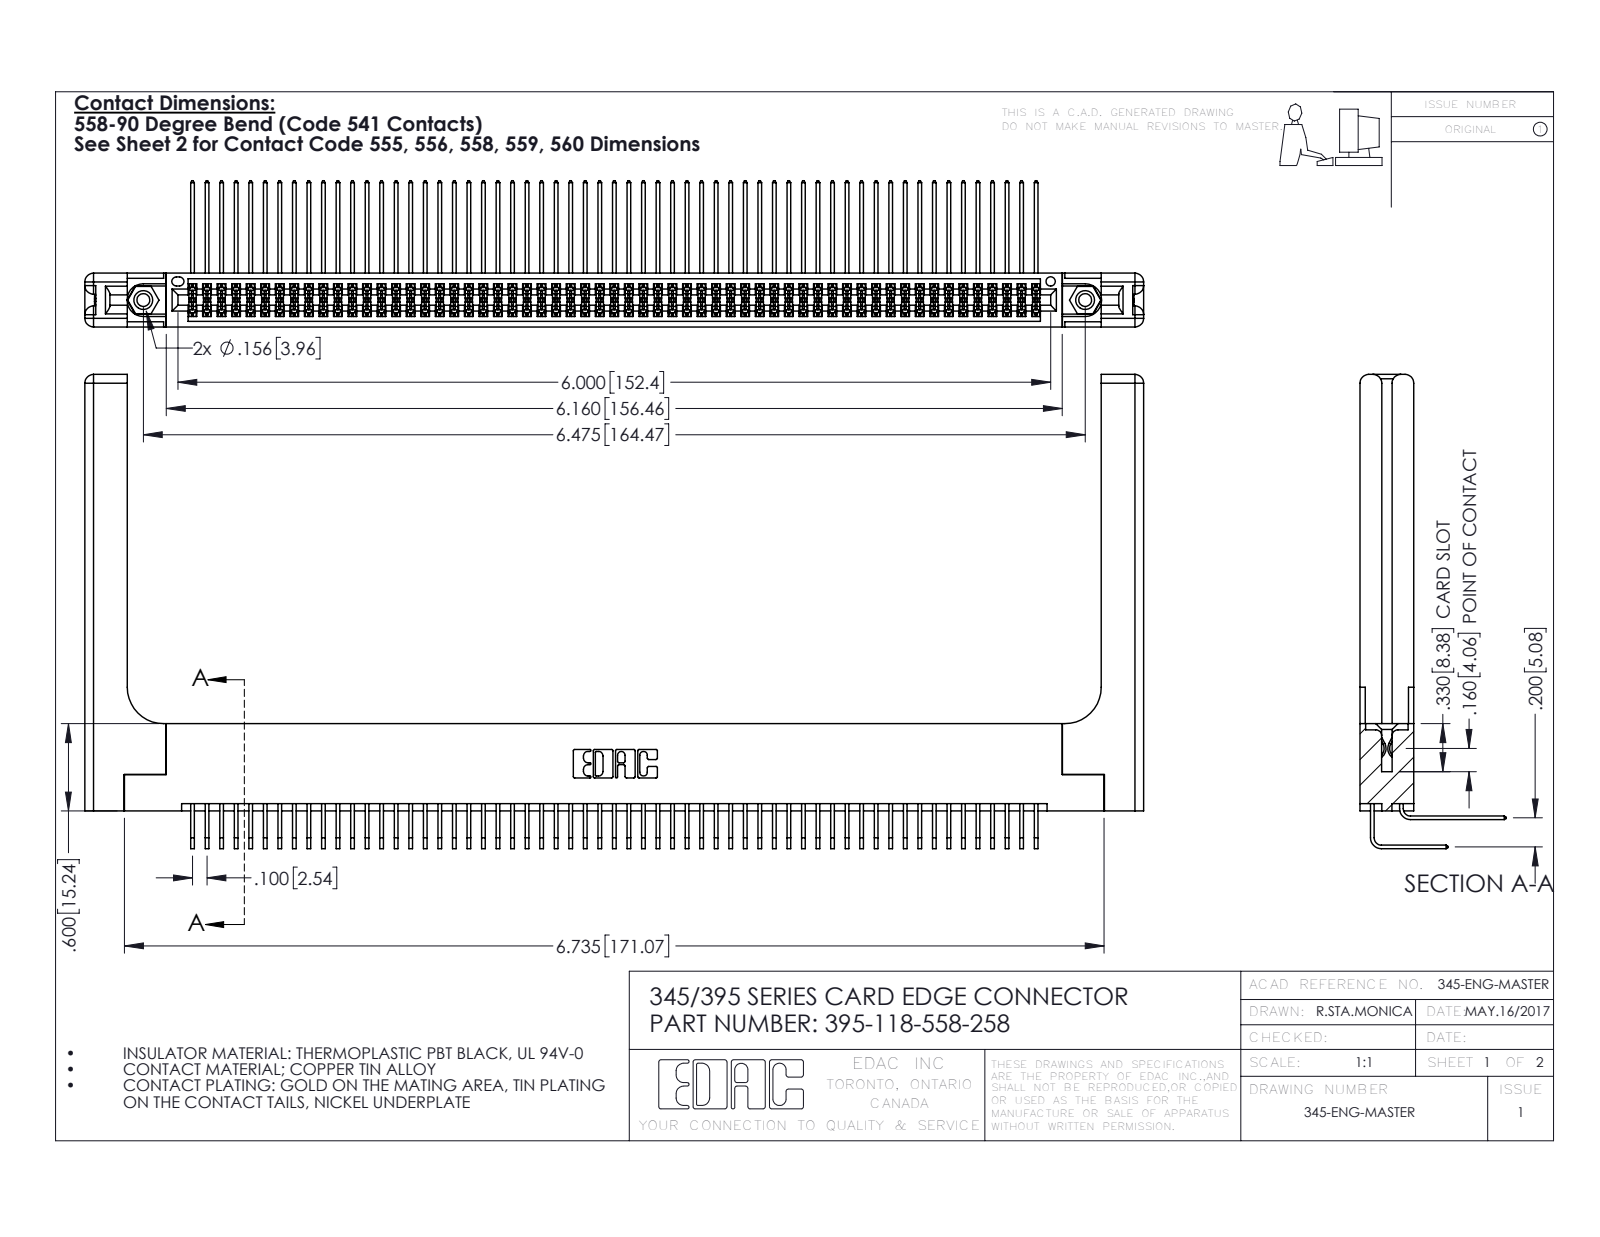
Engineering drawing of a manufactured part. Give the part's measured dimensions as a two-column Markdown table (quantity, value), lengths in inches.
| quantity | value |
| --- | --- |
| part name | 345 Part_Flush Mounting Lugs - 0.156 Dia-TH; 345-292-001_558 559 Tail - 1; 345-250-001_345-250-001-102; 345-292-001_558 Tail - 2 (+2 more) |
| STEP written by | SolidWorks 2016 (CONFIG_CONTROL_DESIGN) |
| units | inches |
| bodies | 123 solids, 6518 faces (4358 planar, 2100 cylindrical, 60 other) |
| overall size | 7.279 × 3.259 × 1.005 |
| volume | 1.664 in³ |
| surface area | 56.38 in² |
| round holes (diameter × count) | 0.089 × 2, 0.125 × 2, 0.156 × 2, 0.064 × 1 |
| round bosses / shafts (diameter × count) | 0.155 × 2 |
| partial cylindrical surfaces (radius × count) | 0.006 × 178, 0.01 × 22, 0.06 × 16, 0.007 × 6, 0.031 × 6, 0.026 × 3, 0.014 × 2, 0.019 × 2 |
| main face-to-face distances | 0.072, 0.298, 0.37, 0.2, 0.098, 0.272, 0.025, 0.225, 0.148, 0.15 |
| hole center spacings | 0.27, 6.239, 6.475 |
